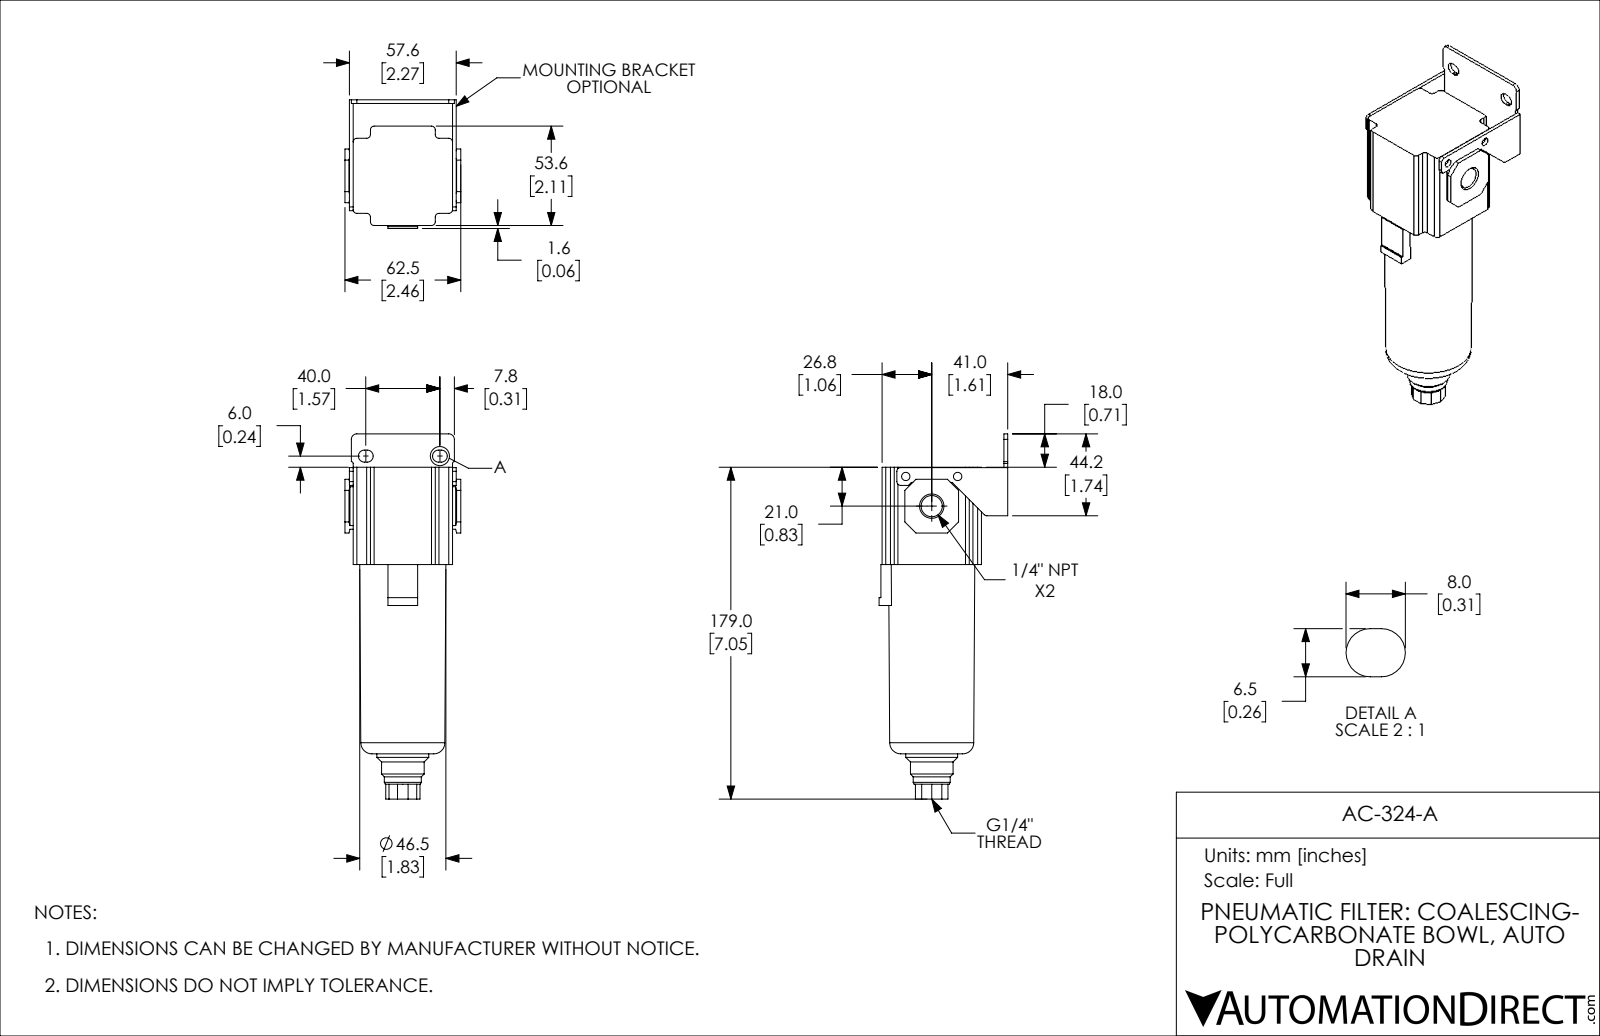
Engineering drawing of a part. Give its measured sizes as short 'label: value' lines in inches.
name: AC-324-A
written by: SolidWorks 2018 (AUTOMOTIVE_DESIGN)
unit: in
bodies: 1 solid, 173 faces (109 planar, 48 cylindrical, 16 other)
size: 7.756 × 2.733 × 2.461
volume: 20 in³; area: 65.25 in²
holes: 2× ⌀0.177, 2× ⌀0.451
bosses: 1× ⌀1.102, 1× ⌀0.906, 1× ⌀0.787
rounds: 15× R0.079, 4× R0.128, 2× R0.039, 2× R0.118
face distances: 0.079, 2.11, 2.189, 0.559, 2.669, 0.48, 2.591, 0.096, 0.175, 2.285
hole spacings: 0.837, 1.102
